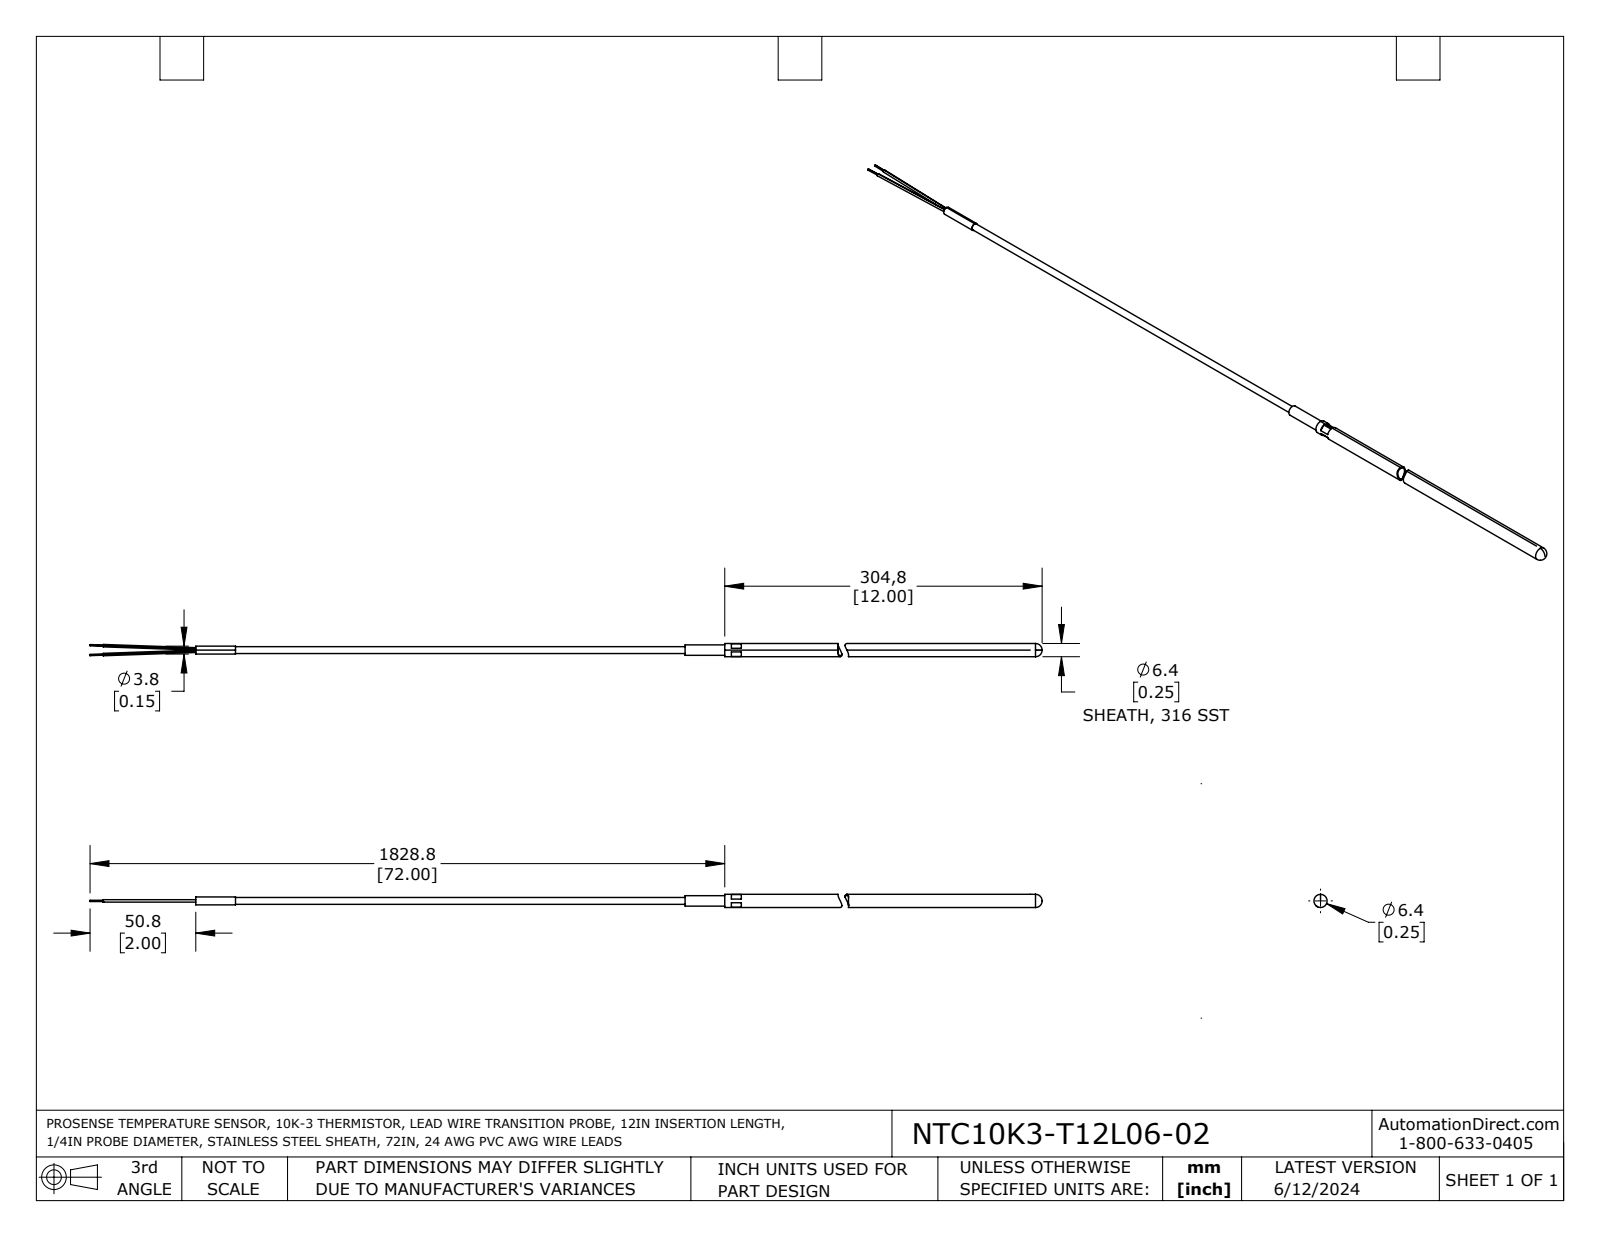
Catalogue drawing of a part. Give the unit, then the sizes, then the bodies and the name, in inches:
Units: inches
Overall size (bounding box): 23.995 × 0.25 × 0.25
Round holes (diameter × count): ⌀0.131 ×1, ⌀0.187 ×1, ⌀0.21 ×1
Round bosses / shafts (diameter × count): ⌀0.25 ×1, ⌀0.197 ×1, ⌀0.15 ×1, ⌀0.13 ×1
Main face-to-face distances: 0.219, 11.775, 10.001, 21.776, 0.75, 10.126, 0.125, 11.65, 10.314, 0.313
Volume: 0.325 in³ · Surface area: 24.4 in²
Bodies: 3 solids, 49 faces (25 planar, 14 cylindrical, 10 other)
Part name (STEP PRODUCT): NTC10K3-T12L06-02
STEP written by: SolidWorks 2021 (AUTOMOTIVE_DESIGN)
